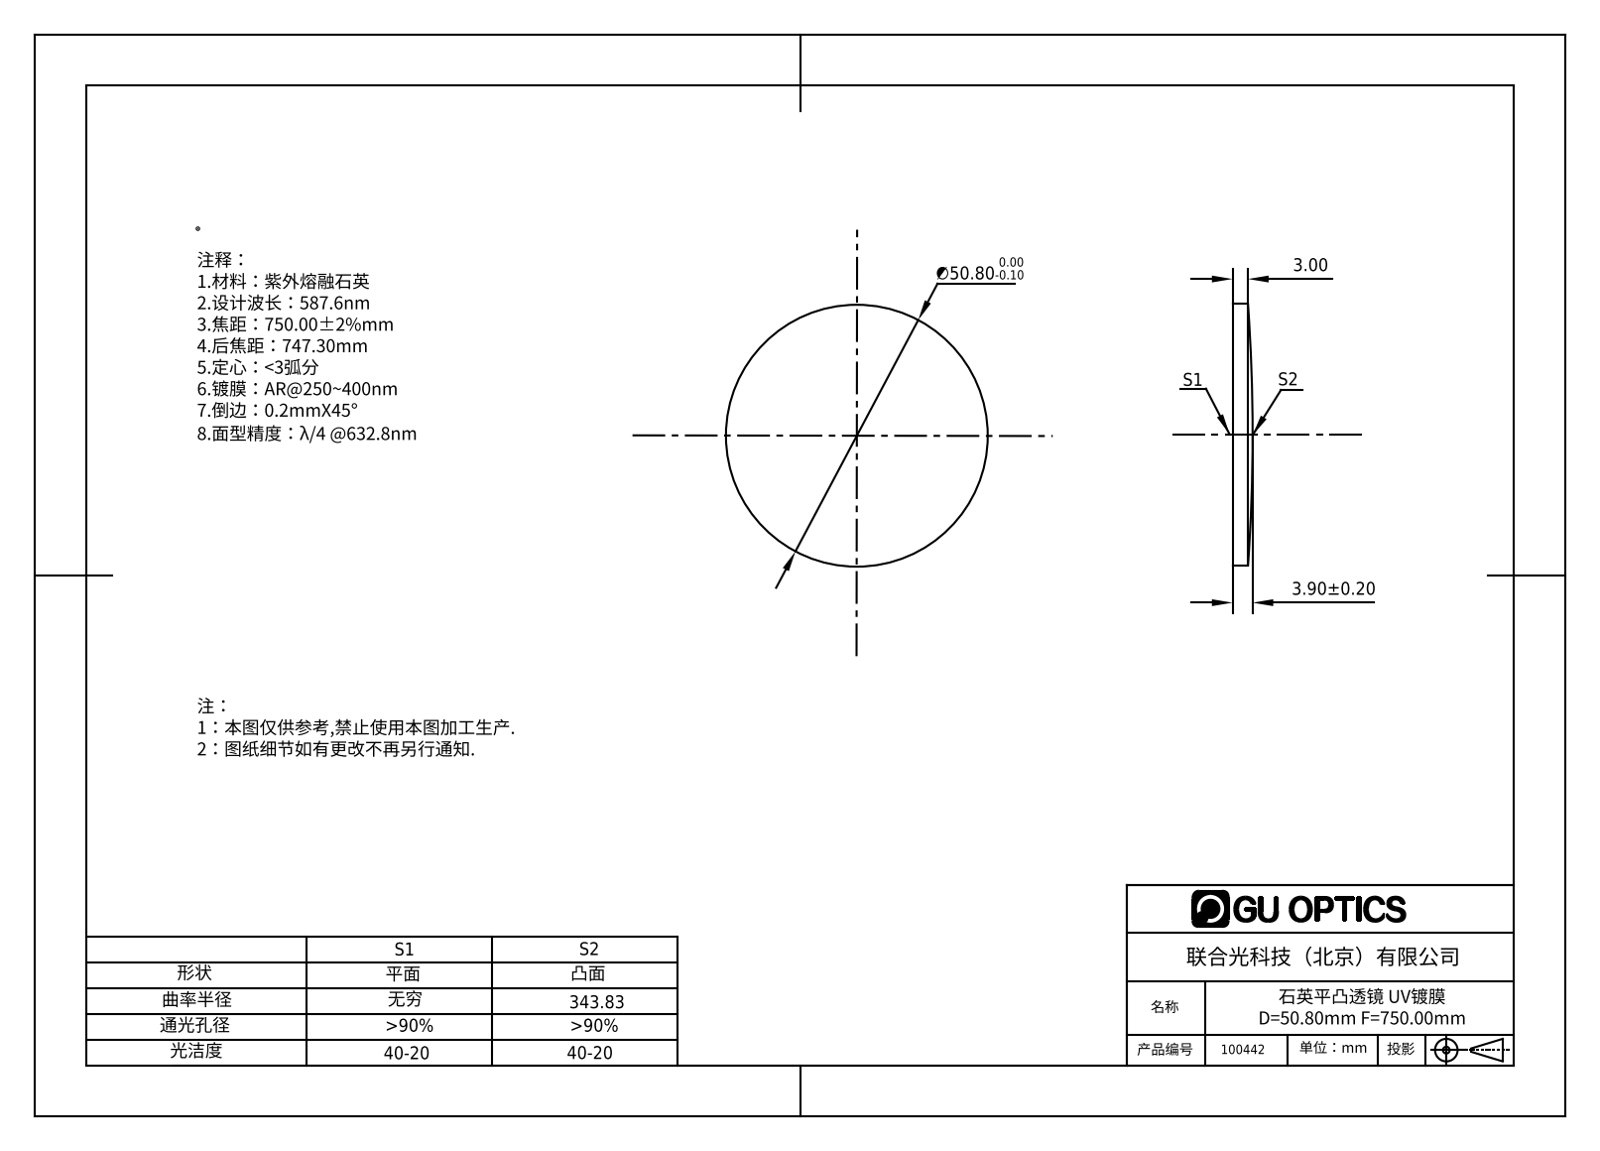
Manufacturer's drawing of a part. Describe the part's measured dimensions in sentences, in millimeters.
The part is named "100392". Its 3-D file was written by "SolidWorks 2016 (AUTOMOTIVE_DESIGN)". It is 1 solid with 5 faces: 1 planar, 2 cylindrical and 2 other. Overall it measures 50.8 by 50.8 by 3.9 millimeters. Its volume is 6 993 cubic millimeters and its surface area 4 535 square millimeters. Round bosses or shafts: 1 of diameter 50.8.
